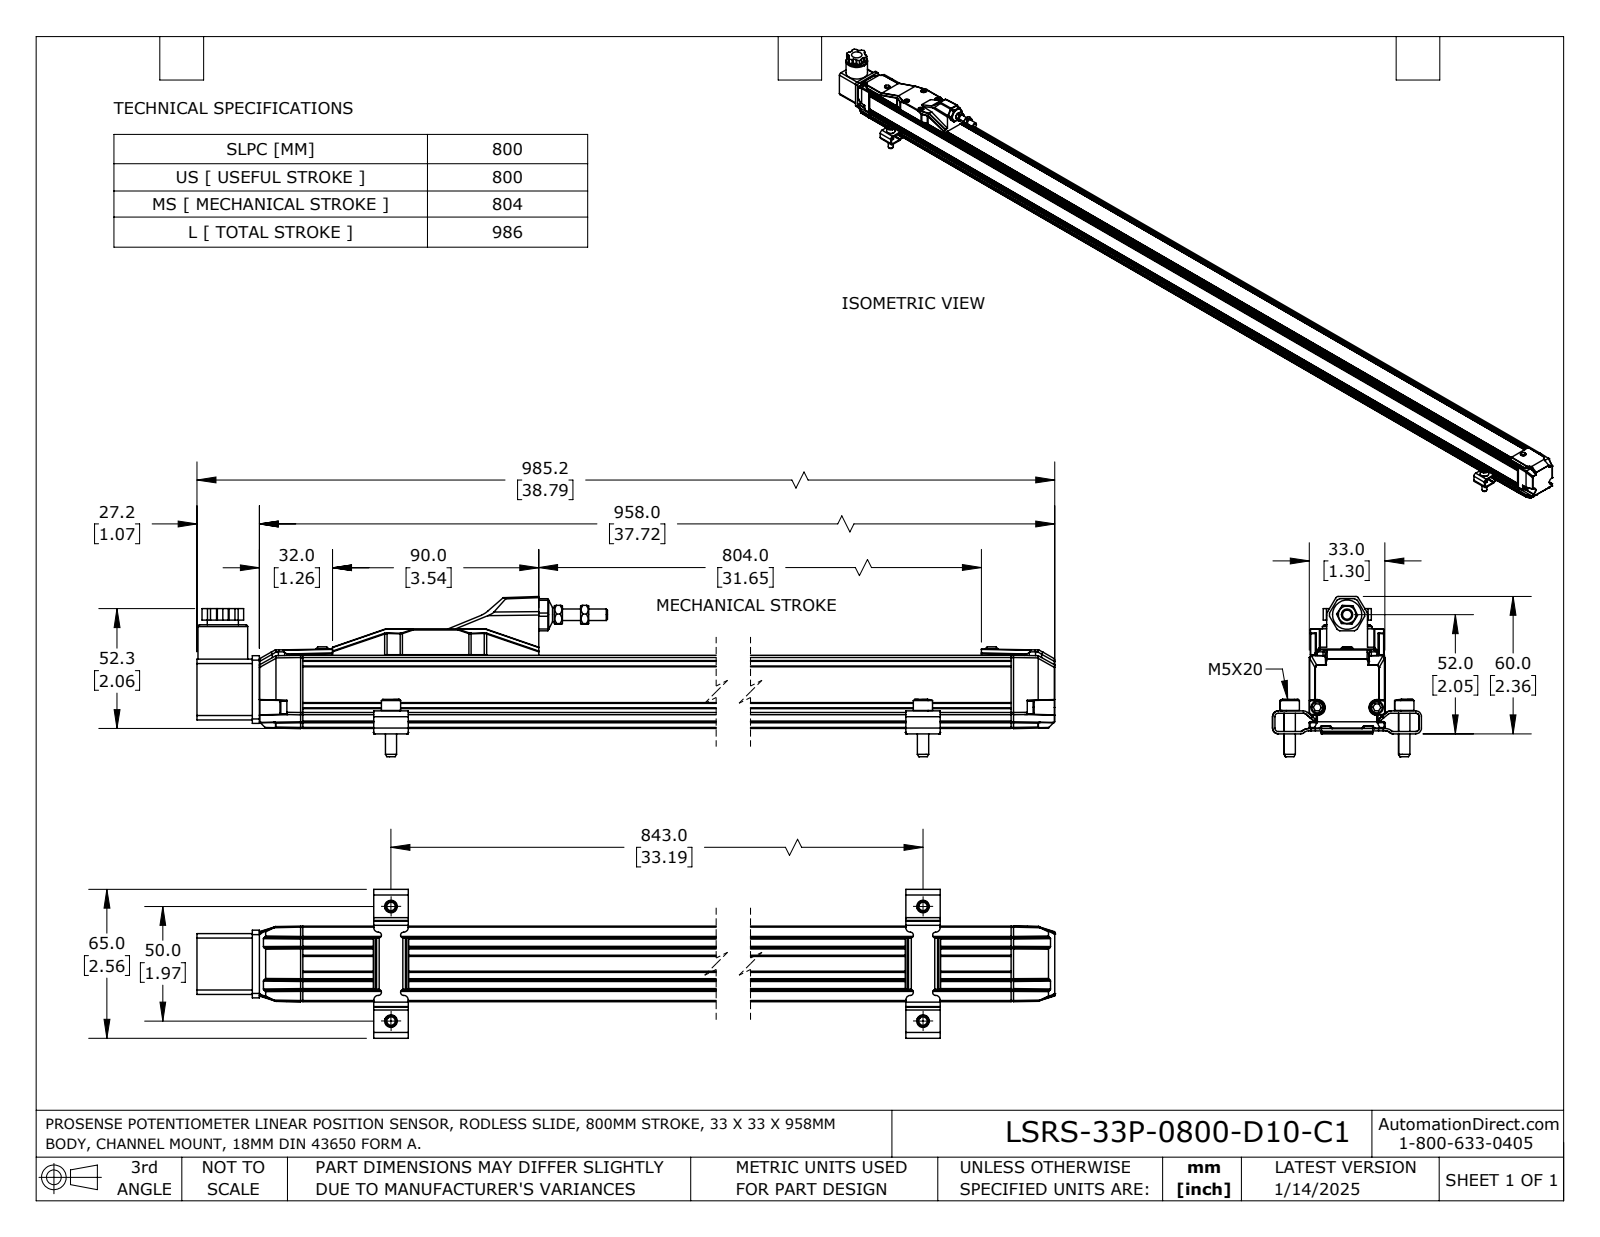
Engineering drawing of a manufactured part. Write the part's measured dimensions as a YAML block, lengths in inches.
part_name: "LSRS-33P-0800-D10-C1"
step_written_by: "SolidWorks 2023 (AUTOMOTIVE_DESIGN)"
units: inches
bodies: {solids: 11, faces: 1314, planar: 823, cylindrical: 359, other: 132}
overall_size: [38.787, 2.754, 2.559]
volume: 56.98
surface_area: 335.6
round_holes:
  - {diameter: 0.185, count: 4}
  - {diameter: 0.217, count: 4}
  - {diameter: 0.106, count: 2}
  - {diameter: 0.13, count: 2}
  - {diameter: 0.157, count: 1}
  - {diameter: 0.197, count: 1}
  - {diameter: 0.209, count: 1}
  - {diameter: 0.232, count: 1}
  - {diameter: 0.236, count: 1}
  - {diameter: 0.276, count: 1}
  - {diameter: 0.394, count: 1}
  - {diameter: 0.413, count: 1}
round_bosses_or_shafts:
  - {diameter: 0.331, count: 4}
  - {diameter: 0.193, count: 4}
  - {diameter: 0.181, count: 4}
  - {diameter: 0.113, count: 4}
  - {diameter: 0.22, count: 2}
  - {diameter: 0.217, count: 2}
  - {diameter: 0.118, count: 2}
  - {diameter: 0.098, count: 2}
partial_cylinders:
  - {radius: 0.02, count: 78}
  - {radius: 0.008, count: 62}
  - {radius: 0.079, count: 44}
  - {radius: 0.118, count: 26}
  - {radius: 0.039, count: 10}
  - {radius: 0.051, count: 8}
  - {radius: 0.059, count: 8}
  - {radius: 0.157, count: 8}
face_to_face_distances: [1.299, 0.118, 1.244, 1.167, 0.237, 1.007, 0.035, 0.014, 1.285, 0.443]
hole_center_spacings: [0.597, 0.787, 0.933, 1.221, 1.286, 1.673, 1.969, 32.032]
